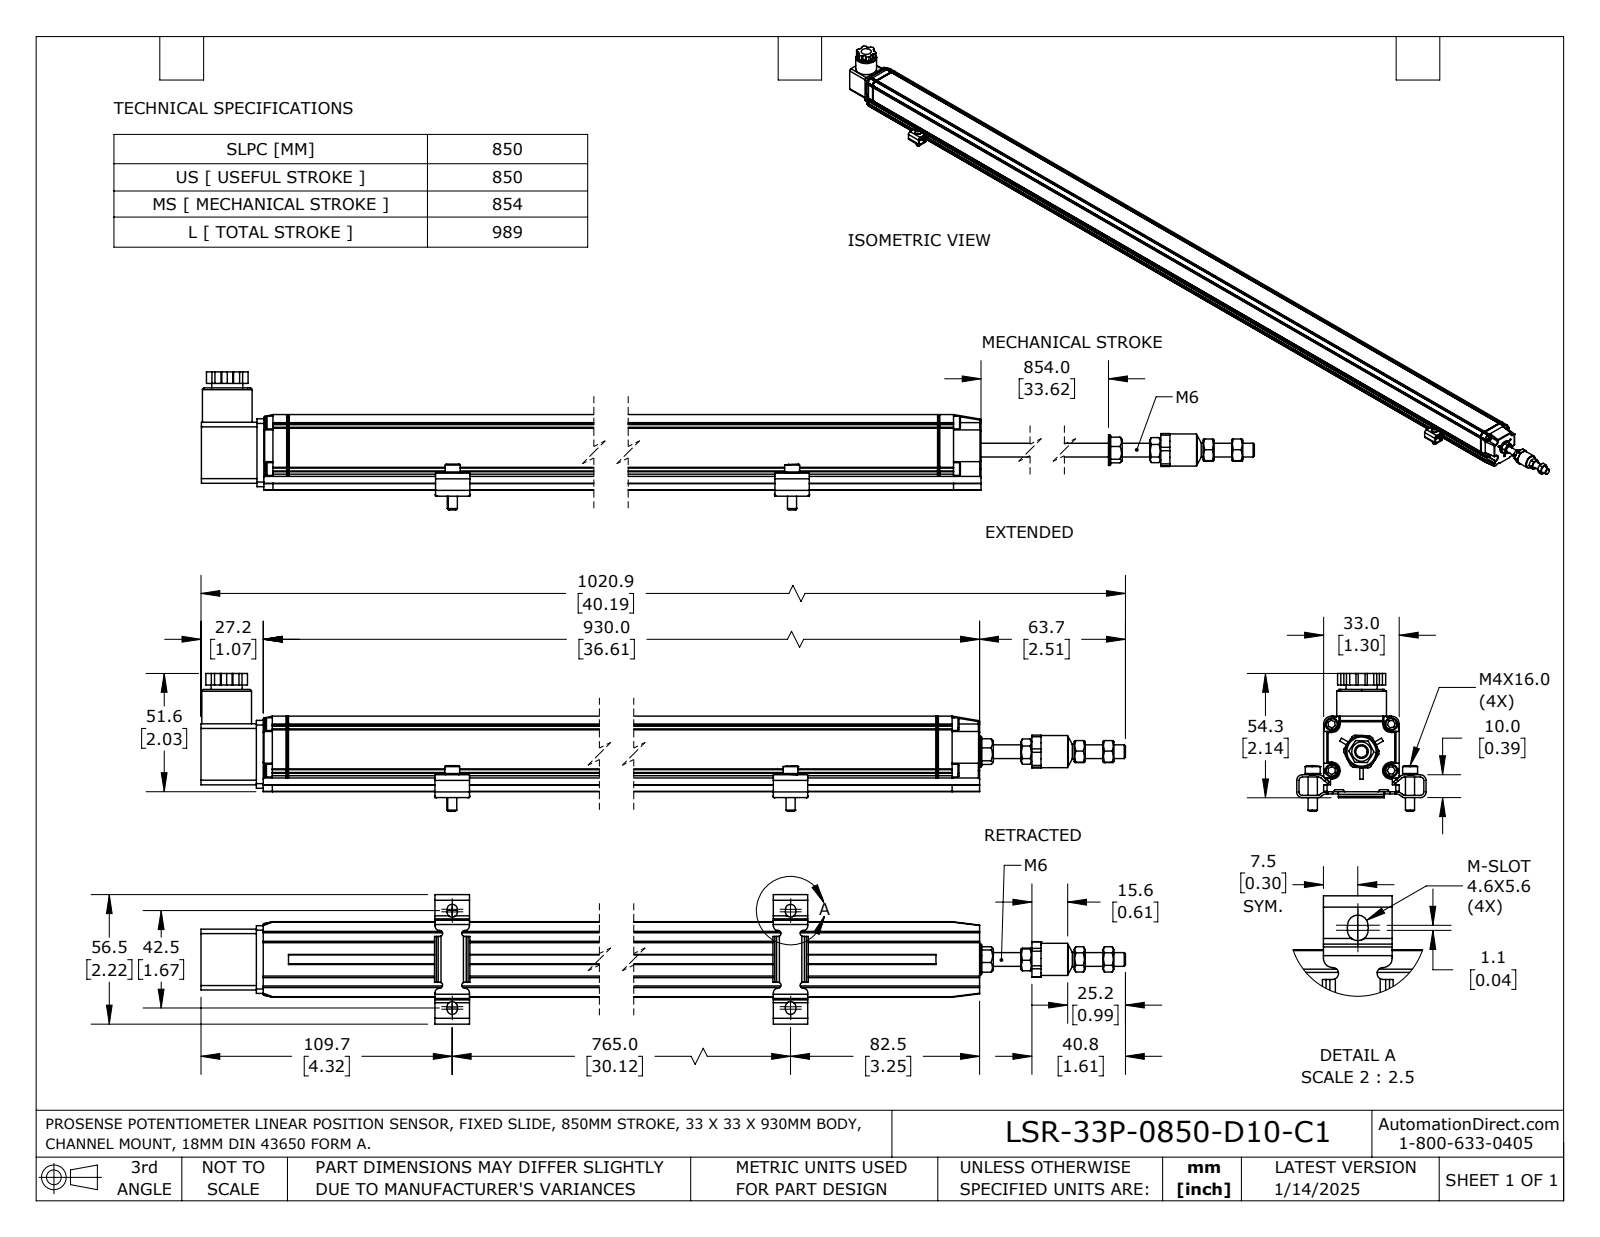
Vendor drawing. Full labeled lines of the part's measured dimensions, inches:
Part name (STEP PRODUCT): LSR-33P-0850-D10-C1
STEP written by: SolidWorks 2023 (AUTOMOTIVE_DESIGN)
Units: inches
Bodies: 14 solids, 995 faces (641 planar, 269 cylindrical, 85 other)
Overall size (bounding box): 40.191 × 2.37 × 2.224
Volume: 56.73 in³ · Surface area: 336.5 in²
Round holes (diameter × count): ⌀0.106 ×4, ⌀0.13 ×4, ⌀0.169 ×1, ⌀0.205 ×1, ⌀0.209 ×1, ⌀0.232 ×1, ⌀0.276 ×1, ⌀0.285 ×1, ⌀0.394 ×1, ⌀0.413 ×1, ⌀0.573 ×1, ⌀0.602 ×1
Round bosses / shafts (diameter × count): ⌀0.157 ×5, ⌀0.118 ×5, ⌀0.256 ×4, ⌀0.22 ×4, ⌀0.854 ×1, ⌀0.551 ×1, ⌀0.535 ×1, ⌀0.528 ×1
Partial cylindrical surfaces — rounded edges, fillets, slot ends (radius × count): R0.079 ×28, R0.02 ×23, R0.008 ×16, R0.051 ×8, R0.059 ×8, R0.089 ×8, R0.118 ×8, R0.039 ×4
Main face-to-face distances: 1.299, 0.118, 0.22, 1.181, 1.079, 0.039, 0.079, 0.142, 1.22, 0.185
Hole centre spacings: 0.047, 0.583, 0.607, 0.696, 0.73, 0.799, 1.024, 1.299
